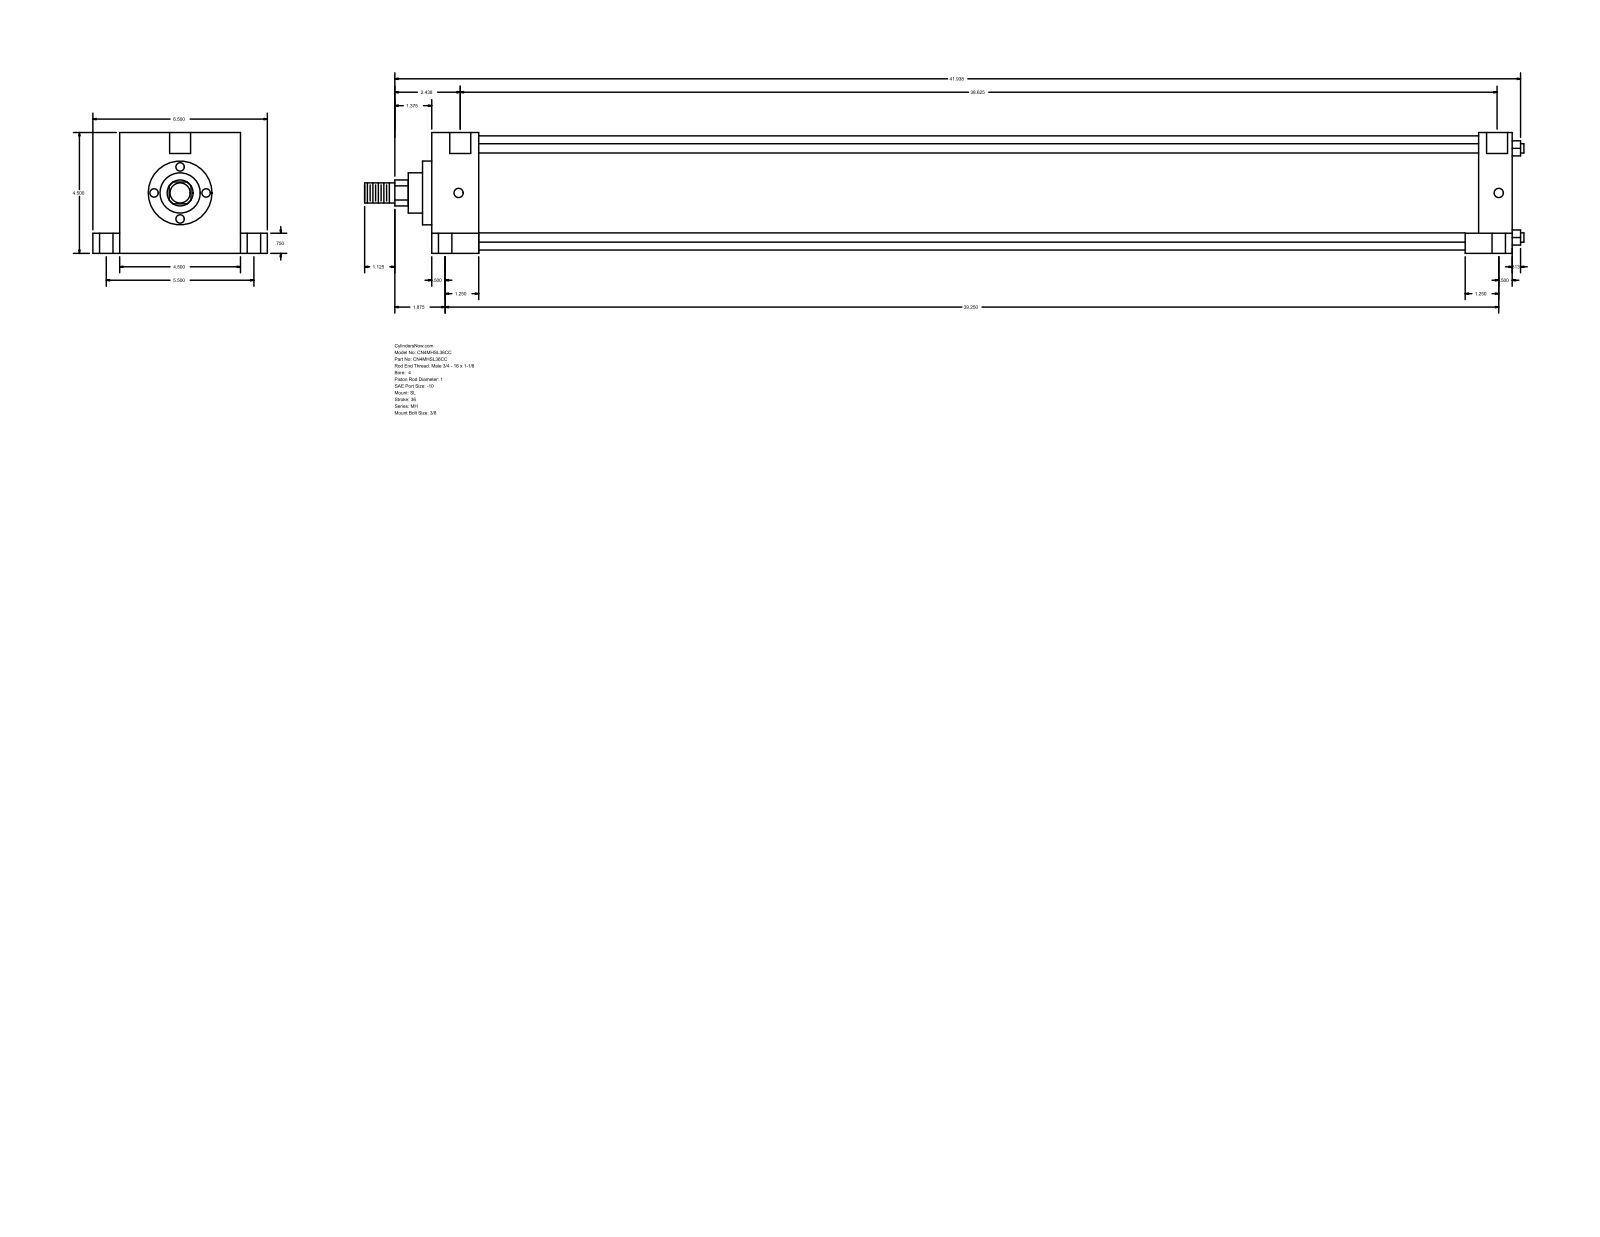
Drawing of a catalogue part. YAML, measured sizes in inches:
part_name: "MH_SL__0400_1"
step_written_by: "GSSL Pune (CONFIG_CONTROL_DESIGN)"
units: inches
bodies: {solids: 0, faces: 110, planar: 77, cylindrical: 33, other: 0}
overall_size: [43.187, 6.5, 4.5]
round_holes:
  - {diameter: 0.344, count: 4}
  - {diameter: 0.5, count: 4}
  - {diameter: 0.75, count: 4}
  - {diameter: 0.781, count: 2}
round_bosses_or_shafts:
  - {diameter: 0.345, count: 4}
  - {diameter: 4.25, count: 1}
  - {diameter: 2.375, count: 1}
  - {diameter: 1.5, count: 1}
  - {diameter: 1, count: 1}
  - {diameter: 0.75, count: 1}
partial_cylinders:
  - {radius: 0.484, count: 1}
face_to_face_distances: [4.5, 40.25, 1.75, 38.5, 39, 37.25, 1.25, 1, 5.5, 0.75]
hole_center_spacings: [2.75, 2.751, 2.795, 2.807, 5.5, 38.75, 38.785, 38.848]
